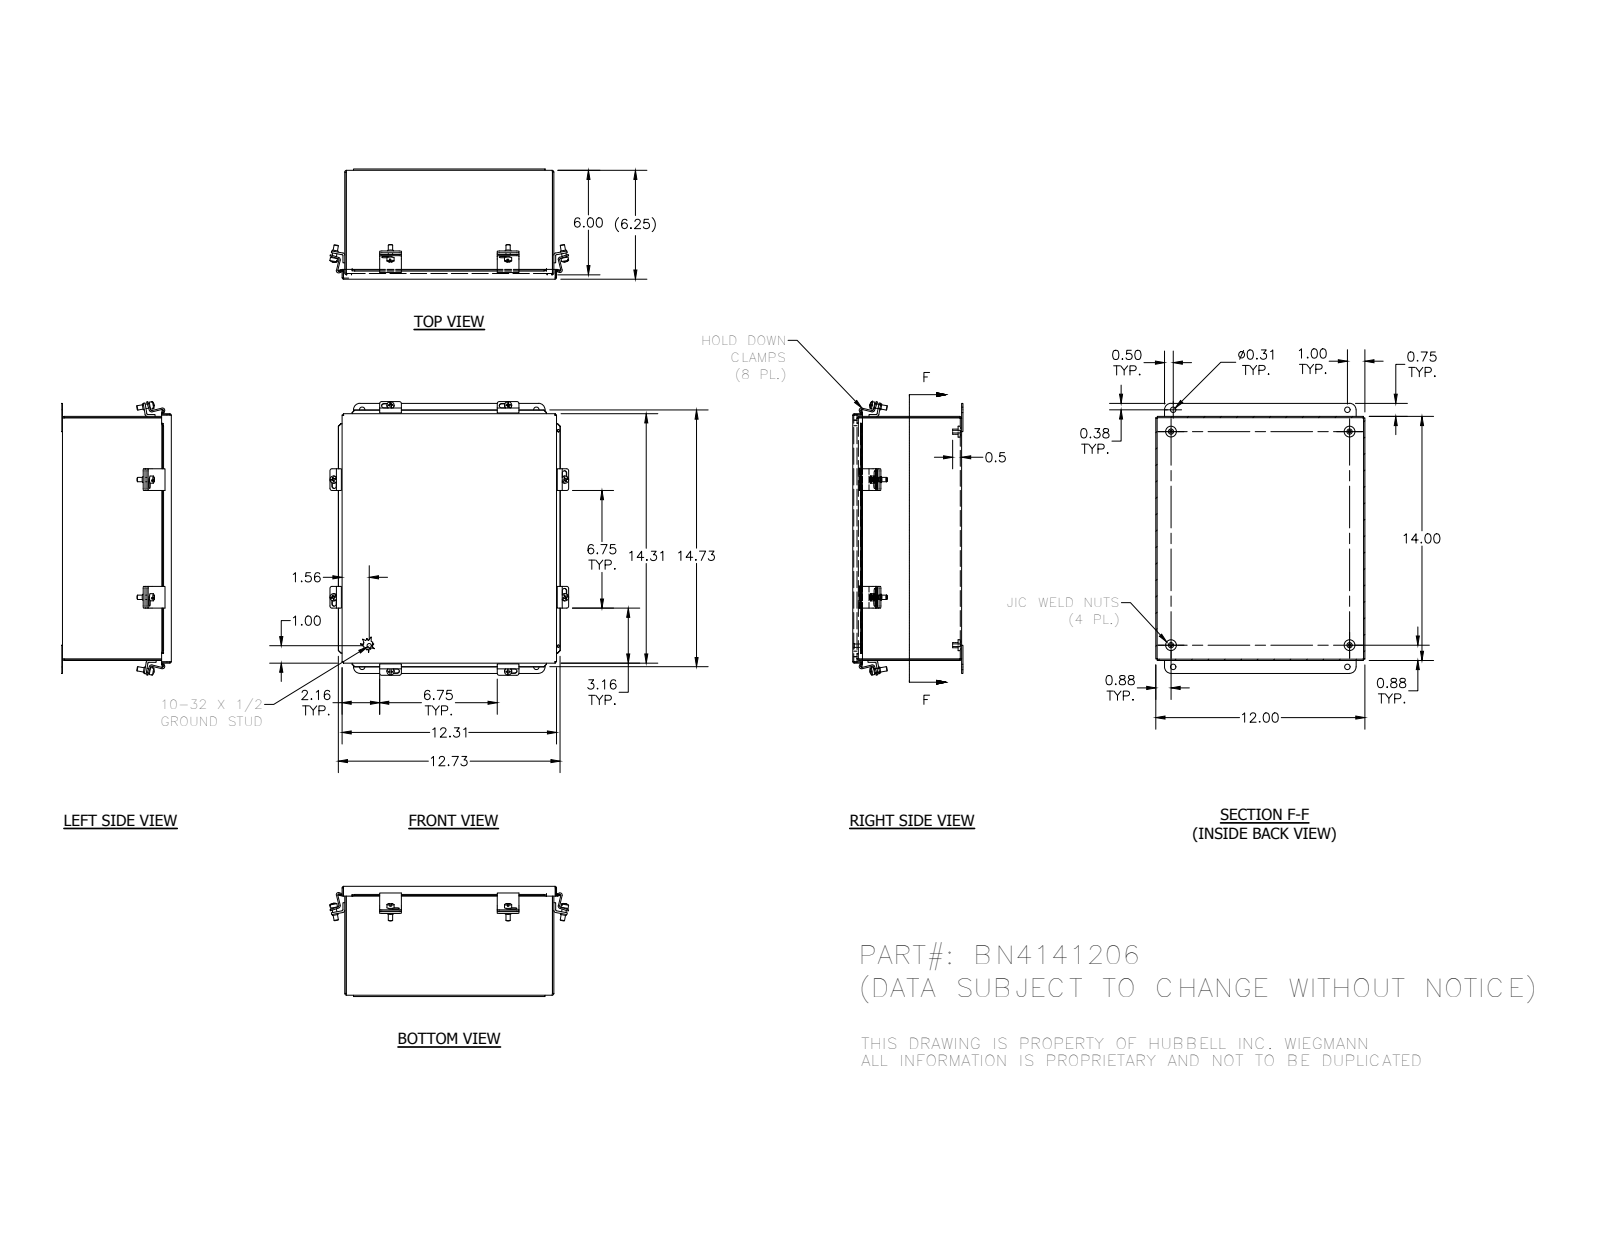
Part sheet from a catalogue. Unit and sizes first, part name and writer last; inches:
Units: inches
Overall size (bounding box): 15.704 × 13.705 × 6.324
Round holes (diameter × count): ⌀0.196 ×8, ⌀0.156 ×4, ⌀0.31 ×4, ⌀0.136 ×2
Round bosses / shafts (diameter × count): ⌀0.25 ×9, ⌀0.41 ×8, ⌀0.344 ×8, ⌀0.625 ×4, ⌀0.3 ×4, ⌀0.19 ×1
Partial cylindrical surfaces — rounded edges, fillets, slot ends (radius × count): R0.125 ×32, R0.031 ×16, R0.133 ×16, R0.063 ×12, R0.126 ×12, R0.093 ×8, R0.105 ×8, R0.375 ×4
Main face-to-face distances: 0.074, 6.187, 0.062, 6.25, 6.113, 6.176, 11.926, 13.926, 12, 11.852
Hole centre spacings: 1.256, 6.75, 13.5, 10, 10.202, 10.202, 10.25, 12.25
Volume: 60.47 in³ · Surface area: 1 634 in²
Bodies: 35 solids, 785 faces (431 planar, 268 cylindrical, 86 other)
Part name (STEP PRODUCT): 316168_1; 3499_1; BN41412LID_1; C1001_1 (+6 more)
STEP written by: SolidWorks 2014 (AUTOMOTIVE_DESIGN)
